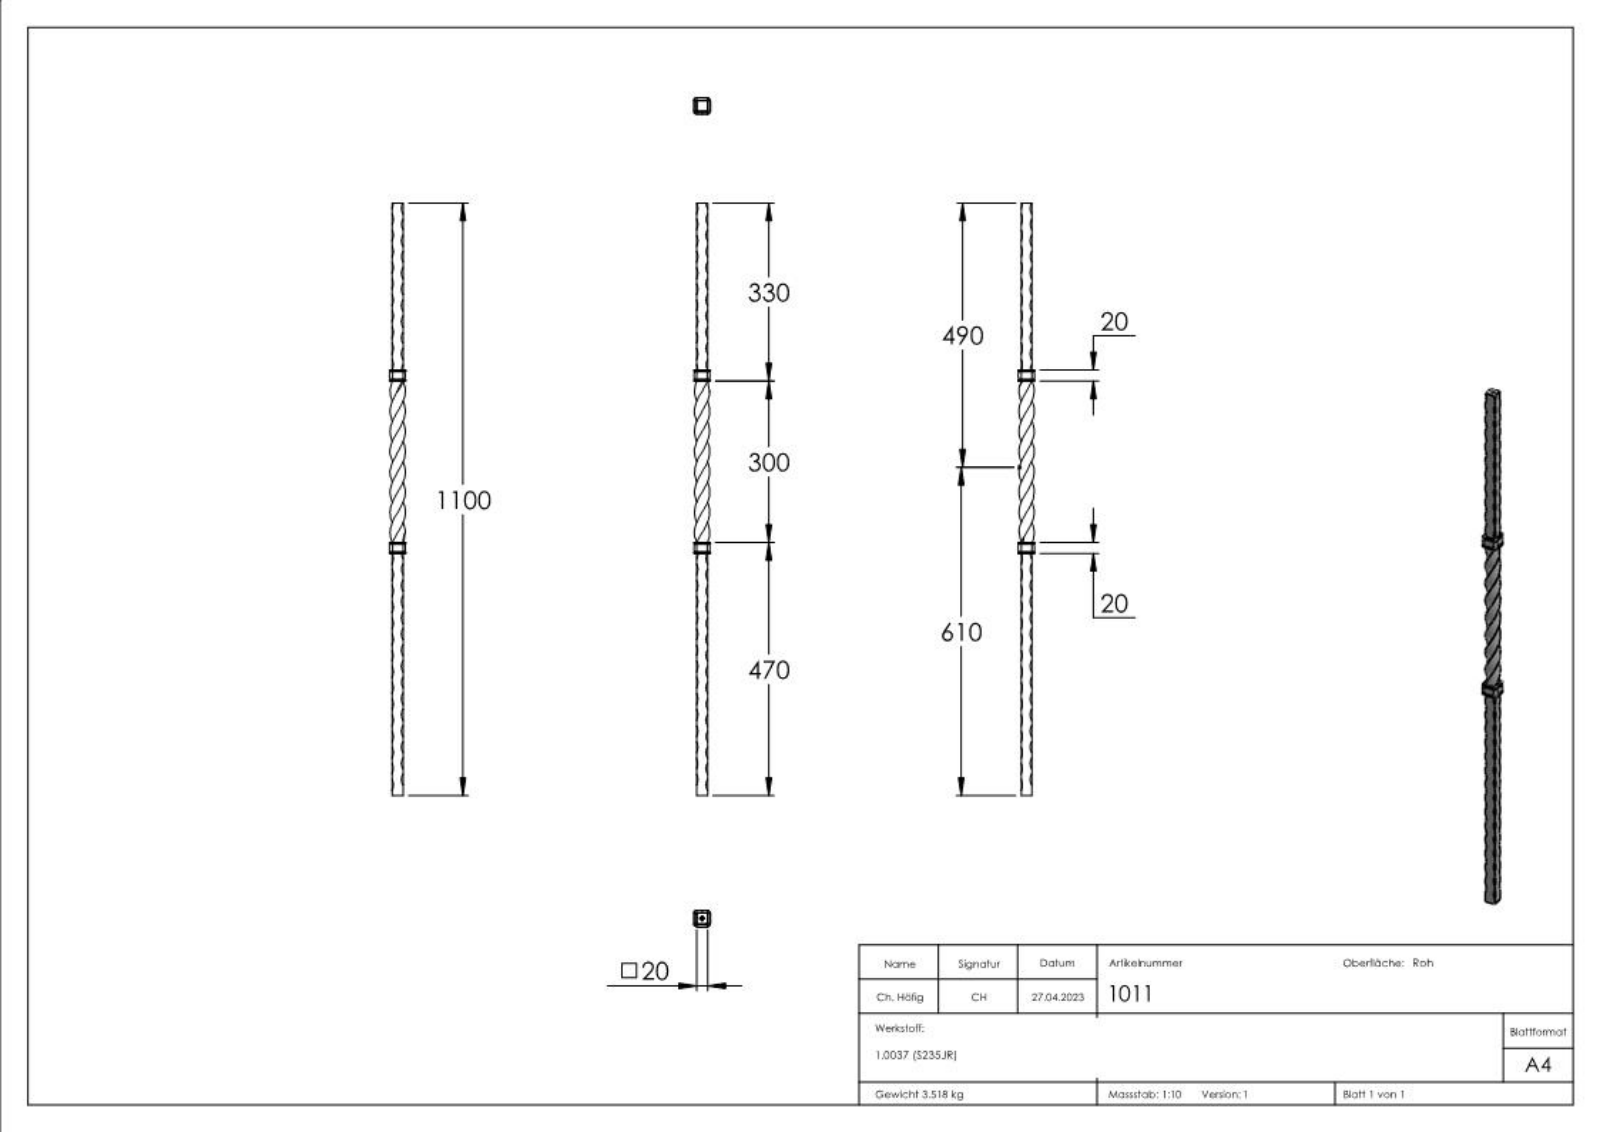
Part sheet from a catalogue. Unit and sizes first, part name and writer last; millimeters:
Units: millimetres
Overall size (bounding box): 1100 × 30.4 × 30.4
Partial cylindrical surfaces — rounded edges, fillets, slot ends (radius × count): R0.2 ×64, R19.5 ×8, R0.5 ×4, R5.5 ×4
Main face-to-face distances: 20, 20.2, 20.4, 320, 5, 5.2, 25.2, 25.4, 300, 340
Volume: 450 998 mm³ · Surface area: 98 053 mm²
Bodies: 3 solids, 600 faces (223 planar, 114 cylindrical, 263 other)
Part name (STEP PRODUCT): 1011
STEP written by: SolidWorks 2018 (CONFIG_CONTROL_DESIGN)
